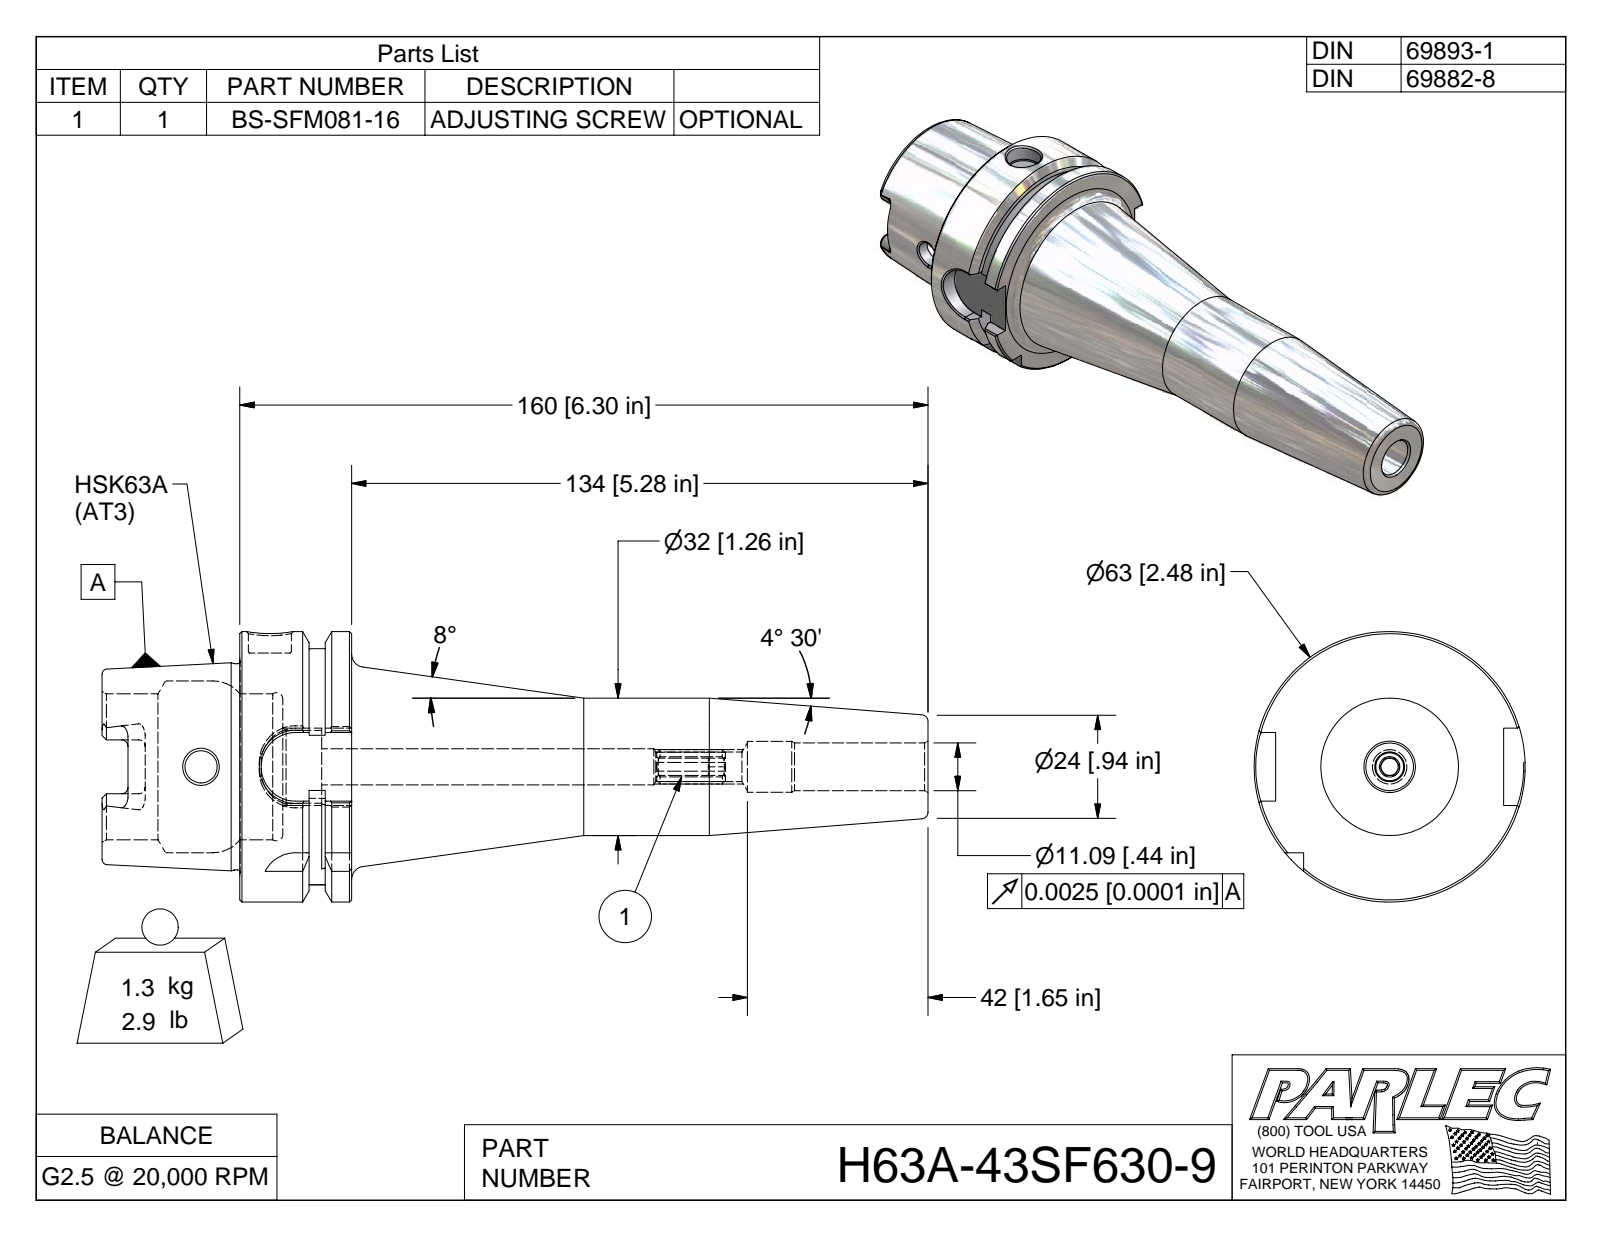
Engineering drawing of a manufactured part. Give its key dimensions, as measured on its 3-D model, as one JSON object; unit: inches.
{"part_name": "H63A-43SF630-9; H63A-43SF630-9-1; BS-SFM081-16", "step_written_by": "Autodesk Inventor 2009 (AUTOMOTIVE_DESIGN)", "units": "inches", "bodies": {"solids": 2, "faces": 160, "planar": 59, "cylindrical": 35, "other": 66}, "overall_size": [7.559, 2.48, 2.48], "volume_in3": 11.94, "surface_area_in2": 61.23, "round_holes": [[0.295, 1], [0.394, 1], [0.437, 1], [0.467, 1], [0.666, 1], [1.339, 1], [1.575, 1]], "round_bosses_or_shafts": [[2.48, 1], [1.891, 1], [1.26, 1]], "partial_cylinders_radius": [[0.059, 6], [0.113, 4], [0.315, 4], [0.157, 1], [1.083, 1]], "face_to_face_distances": [1.024, 0.241, 0.389, 0.394, 0.63, 1.26, 1.654, 2.283, 1.894, 0.635]}
